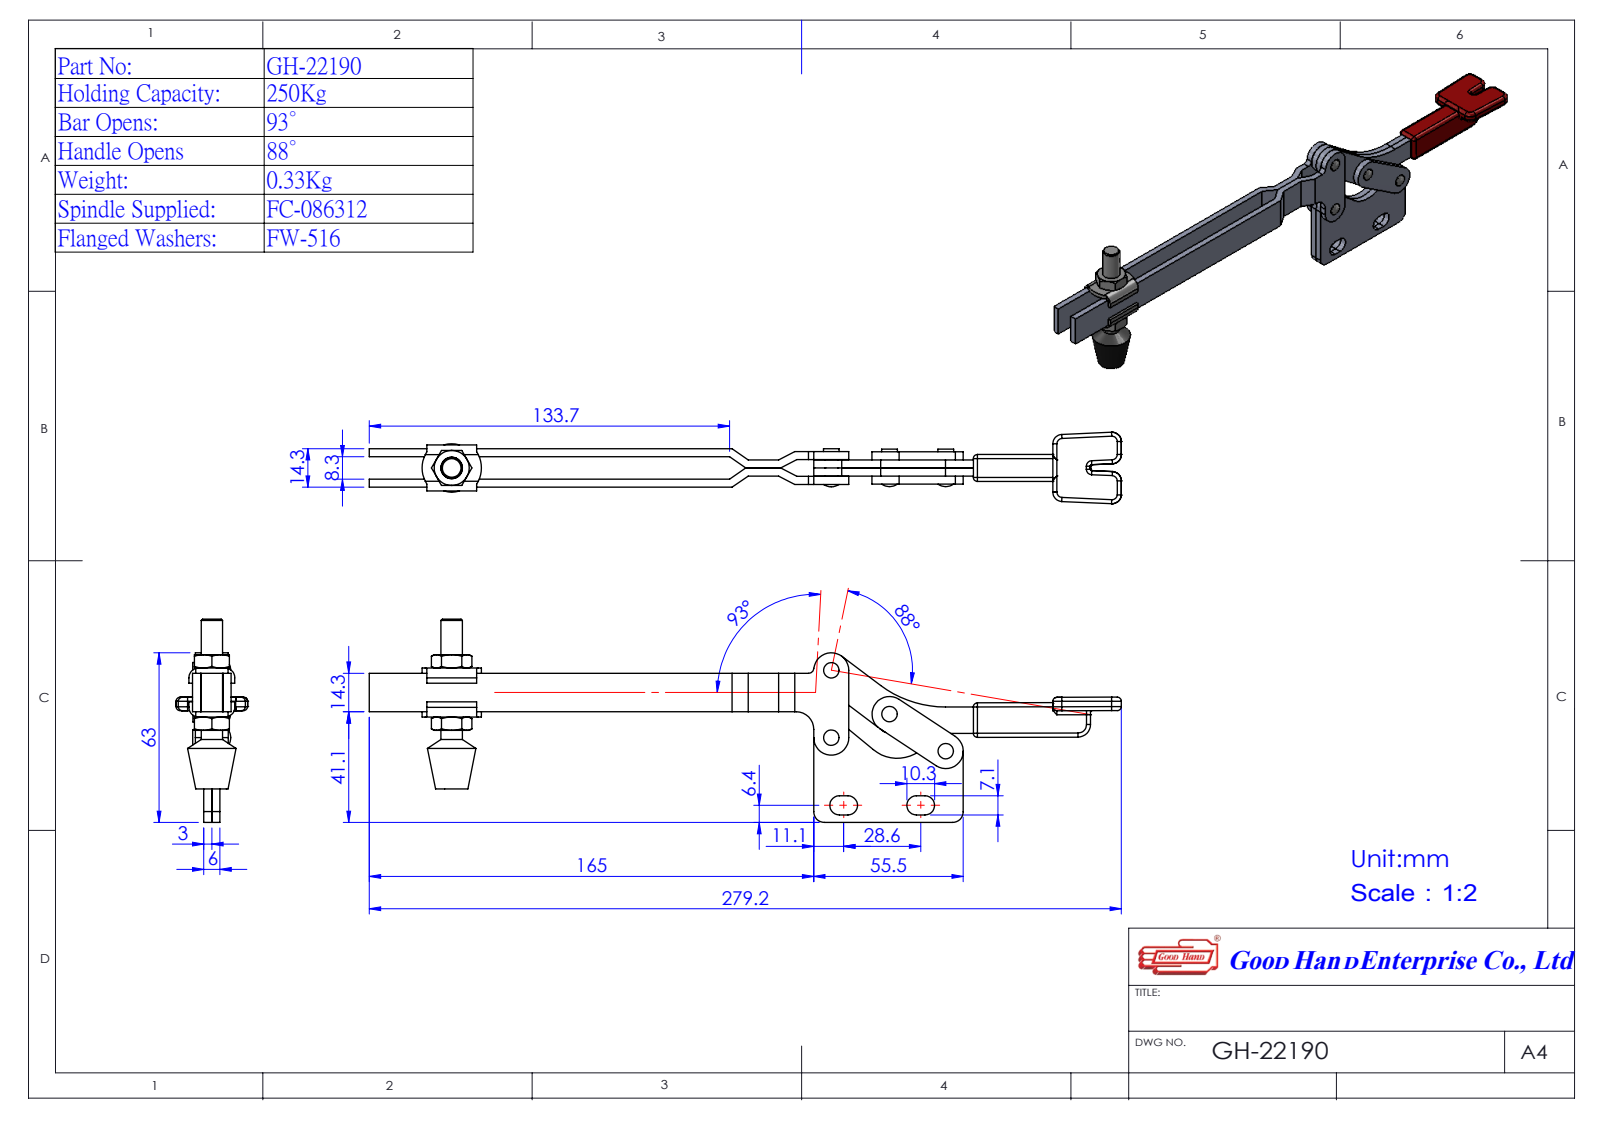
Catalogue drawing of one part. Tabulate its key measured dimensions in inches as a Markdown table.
| quantity | value |
| --- | --- |
| part name | Group1^GH-22185(簡化); Group5^GH-22190(簡化)-1; Group2^GH-22190(簡化)-1; Group1^GH-22170(簡化) (+2 more) |
| STEP written by | SolidWorks 2016 (AUTOMOTIVE_DESIGN) |
| units | inches |
| bodies | 6 solids, 288 faces (150 planar, 100 cylindrical, 38 other) |
| overall size | 10.992 × 2.785 × 1.045 |
| volume | 3.024 in³ |
| surface area | 51.39 in² |
| round holes (diameter × count) | 0.138 × 4, 0.19 × 2 |
| round bosses / shafts (diameter × count) | 0.23 × 4, 0.512 × 1, 0.312 × 1 |
| partial cylindrical surfaces (radius × count) | 0.137 × 6, 0.14 × 4, 0.142 × 4, 0.256 × 4, 0.021 × 2, 0.157 × 2, 0.435 × 2, 0.079 × 1 |
| main face-to-face distances | 0.118, 0.163, 0.281, 0.4, 0.045, 0.445, 0.236, 0.563, 0.041, 0.404 |
| hole center spacings | 0.984, 0.919, 1.065, 1.685, 2.048 |
